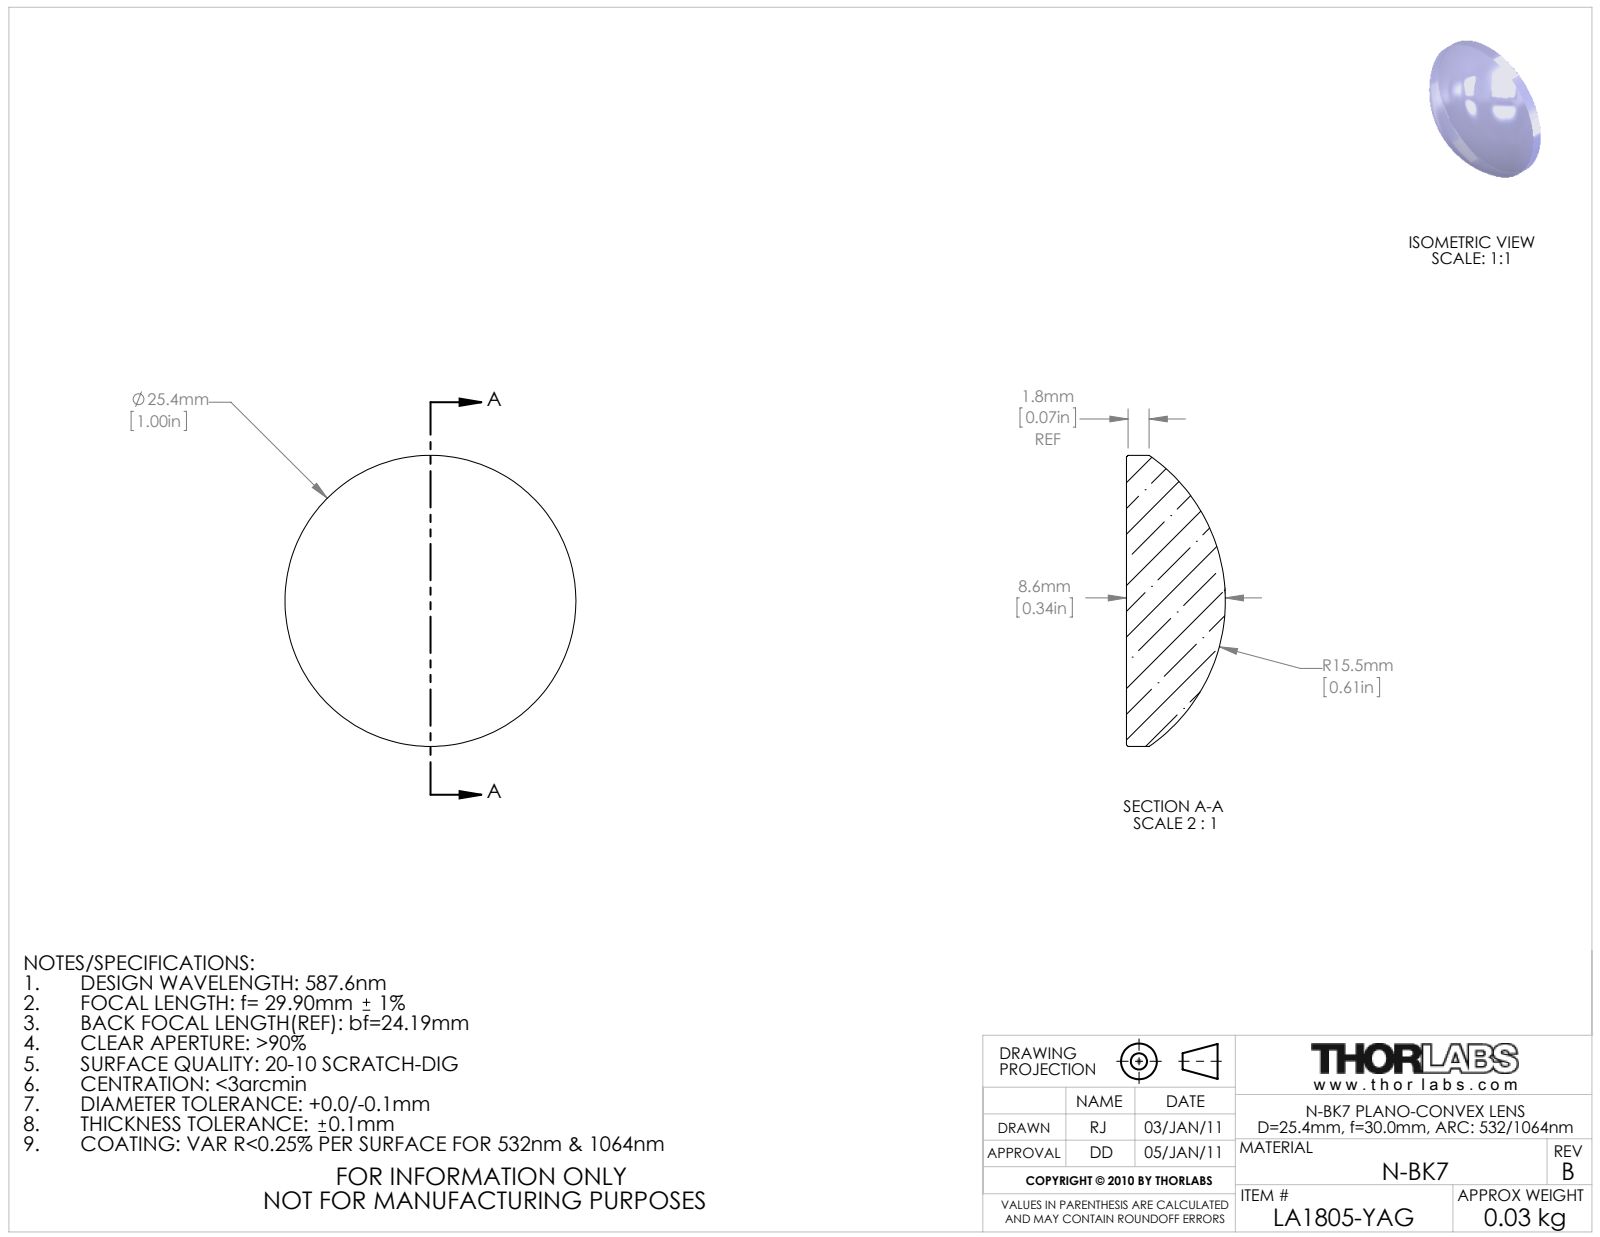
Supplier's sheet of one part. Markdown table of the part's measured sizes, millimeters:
| quantity | value |
| --- | --- |
| part name | 21782-E0W |
| STEP written by | SolidWorks 2011 (AUTOMOTIVE_DESIGN) |
| units | millimeters |
| bodies | 0 solids, 7 faces (1 planar, 2 cylindrical, 4 other) |
| overall size | 25.4 × 25.4 × 8.64 |
| round bosses / shafts (diameter × count) | 25.4 × 1 |
